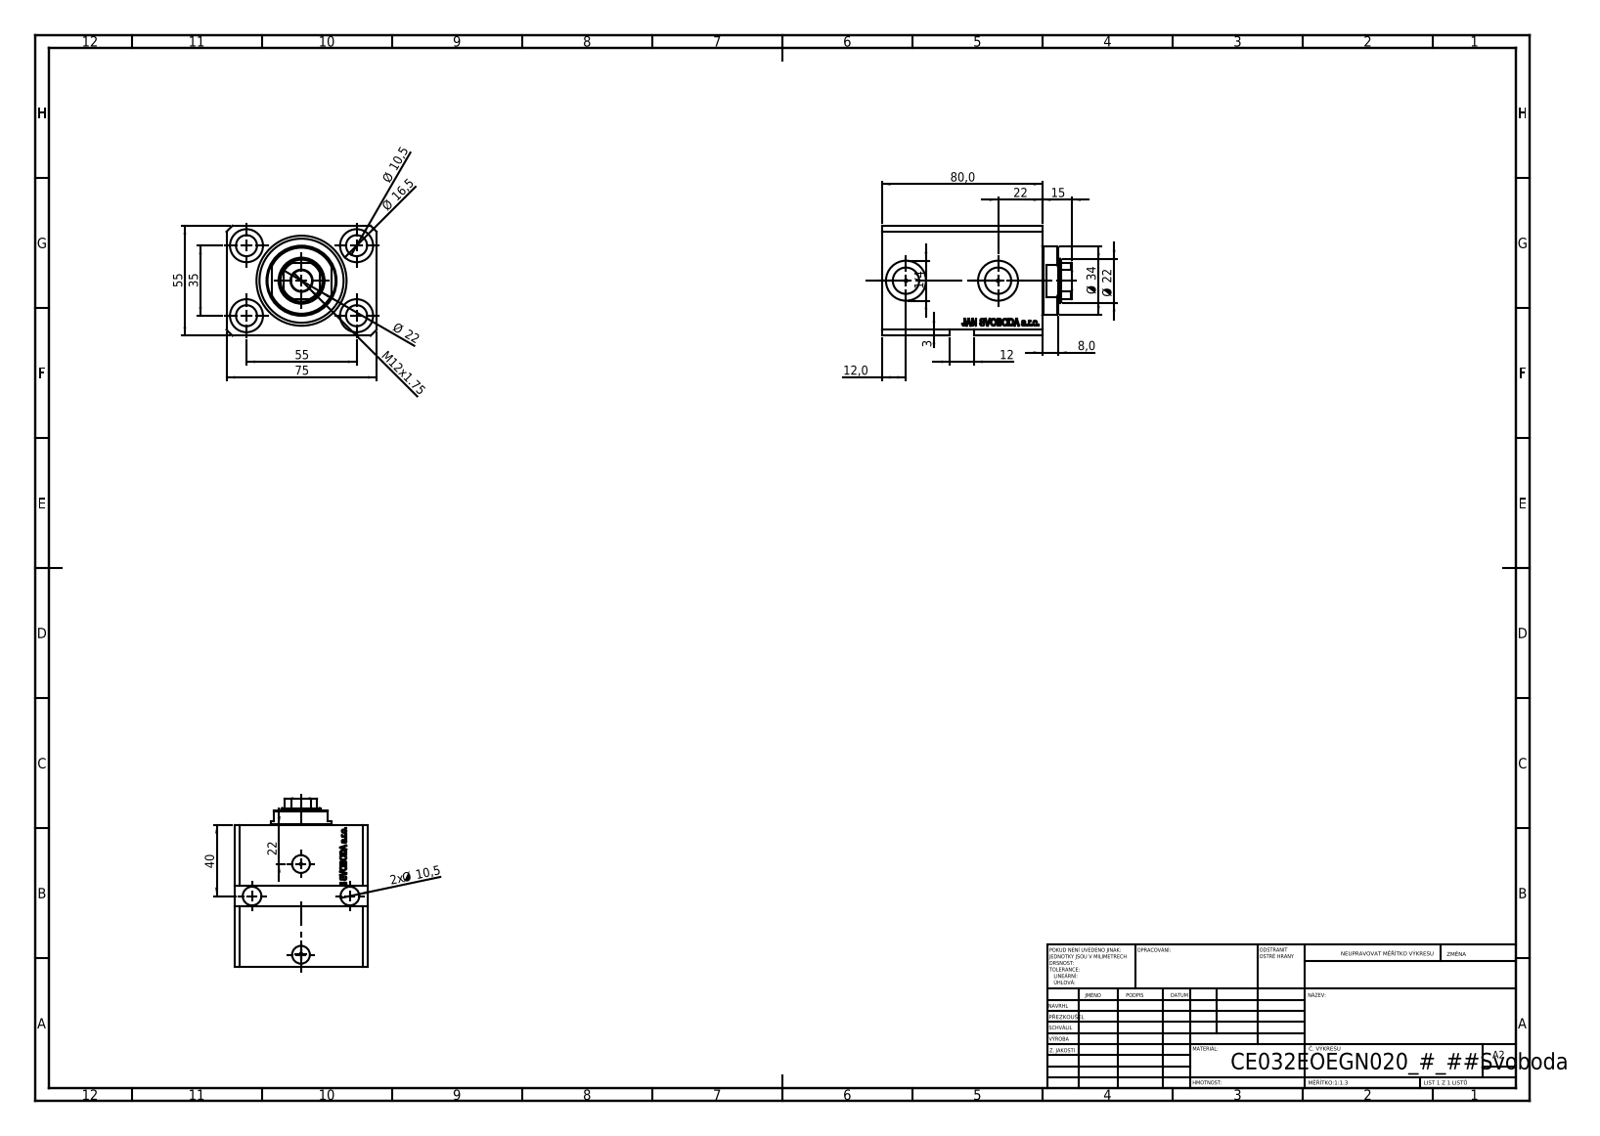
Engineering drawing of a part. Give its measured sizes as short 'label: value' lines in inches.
name: V250CE_E_Body; V250CE_VC_E; V250CE_C_VCP
written by: SolidWorks 2019 (CONFIG_CONTROL_DESIGN)
unit: in
bodies: 3 solids, 894 faces (438 planar, 84 cylindrical, 372 other)
size: 3.74 × 2.953 × 2.165
volume: 16.81 in³; area: 104.2 in²
holes: 7× ⌀0.413, 4× ⌀0.049, 4× ⌀0.65, 2× ⌀0.394, 2× ⌀0.518, 2× ⌀0.787, 1× ⌀0.866, 1× ⌀1.26, 1× ⌀1.772
bosses: 1× ⌀1.339
rounds: 1× R0.413
face distances: 2.165, 2.953, 0.591, 3.15, 2.559, 0.39, 2.169, 2.76, 0.433, 2.717
hole spacings: 1.283, 2.165, 1.294, 1.378, 1.675, 1.691, 2.567, 0.021
